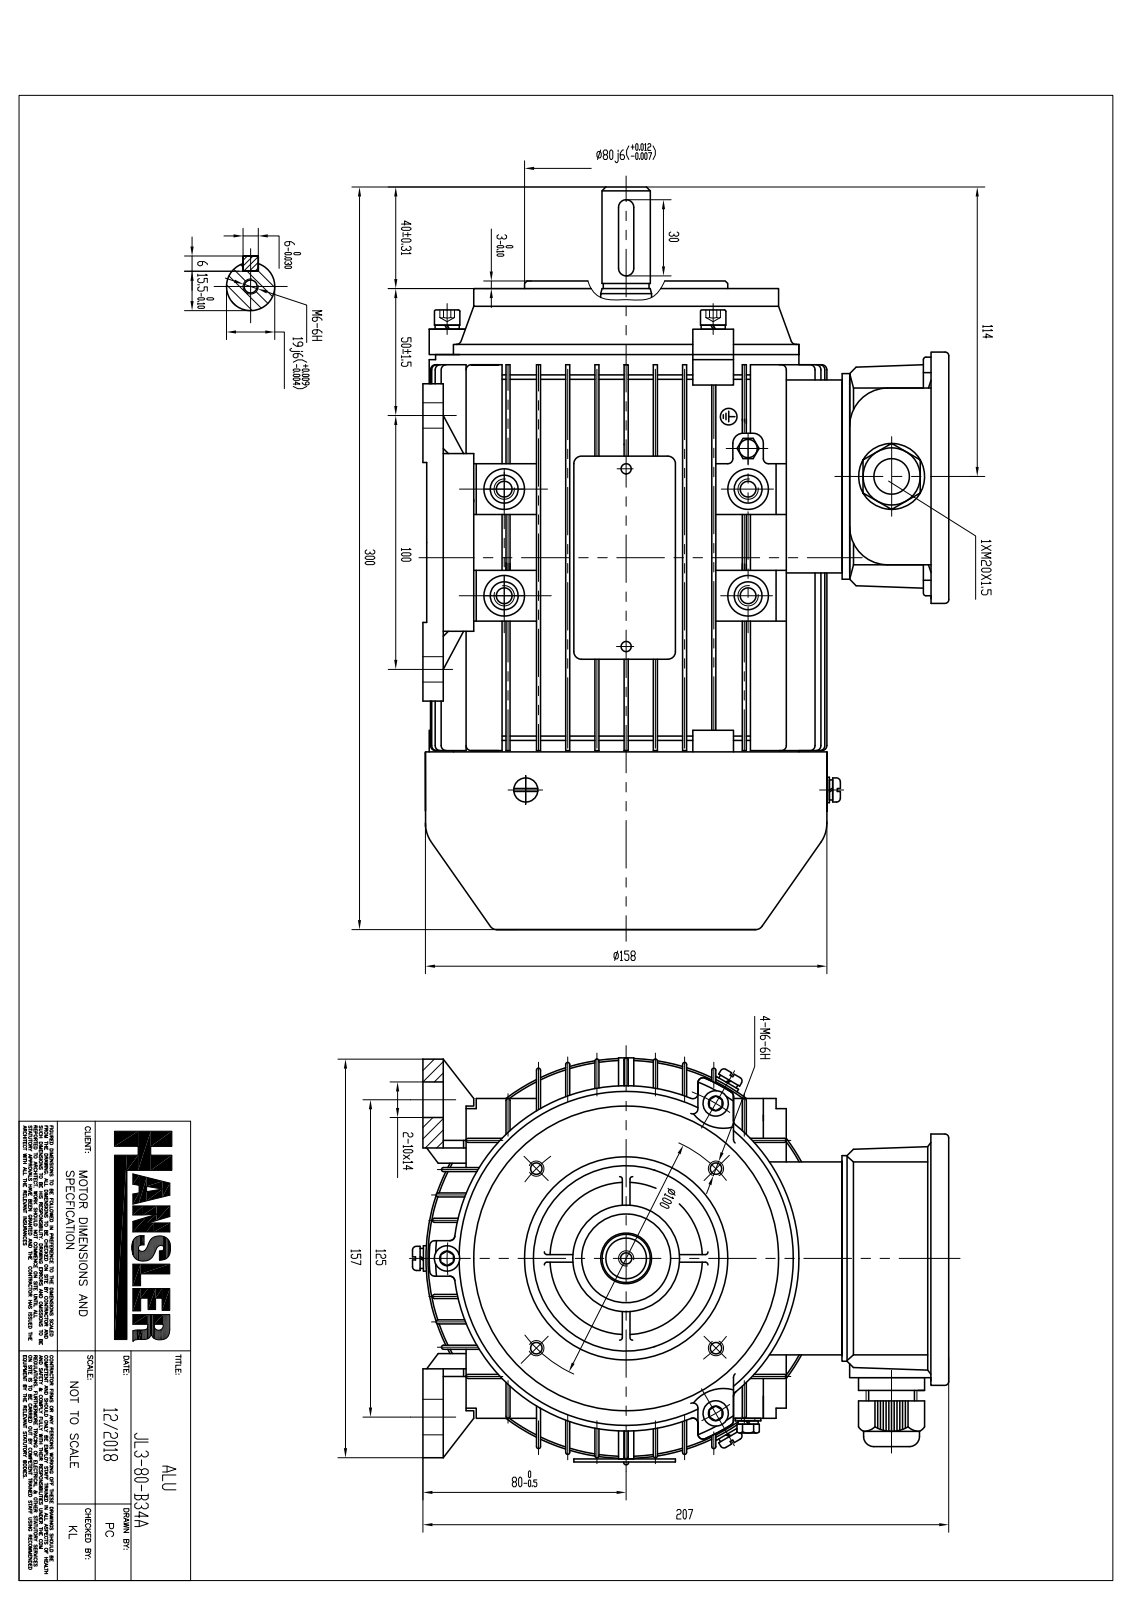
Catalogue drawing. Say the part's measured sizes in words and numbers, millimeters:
The part is named "JL3-80-B34A". Its 3-D file was written by "DATAKIT 2018 (c) (AP242_MANAGED_MODEL_BASED_3D_ENGINEERING_MIM_LF)". It is 48 solids with 2785 faces: 1325 planar, 804 cylindrical and 656 other. Overall it measures 288.99 by 280.27 by 232.96 millimeters. Its volume is 1 160 000 cubic millimeters and its surface area 673 804 square millimeters. Round holes: 13 of diameter 4, 10 of diameter 16, 8 of diameter 6.6, 5 of diameter 6, 4 of diameter 5.25, 4 of diameter 5.3, 4 of diameter 5.8, 4 of diameter 9, 4 of diameter 12, 3 of diameter 6.39, 3 of diameter 7, 2 of diameter 2. Round bosses or shafts: 8 of diameter 11, 5 of diameter 18, 4 of diameter 15, 4 of diameter 13, 4 of diameter 12, 4 of diameter 10, 4 of diameter 8, 4 of diameter 7.85. Partial cylindrical surfaces (rounded edges, fillets, slot ends): 126 of radius 1, 62 of radius 2, 31 of radius 3, 24 of radius 0.33, 20 of radius 5, 16 of radius 0.3, 12 of radius 0.39, 12 of radius 1.97. The main face-to-face distances are 1.6, 11.5, 23, 34.5, 10.57, 46, 9.9, 13.1, 21.14, 21.4. The hole center spacings are 14.14, 42, 54, 87, 96, 104.79, 48.66, 70.5.
